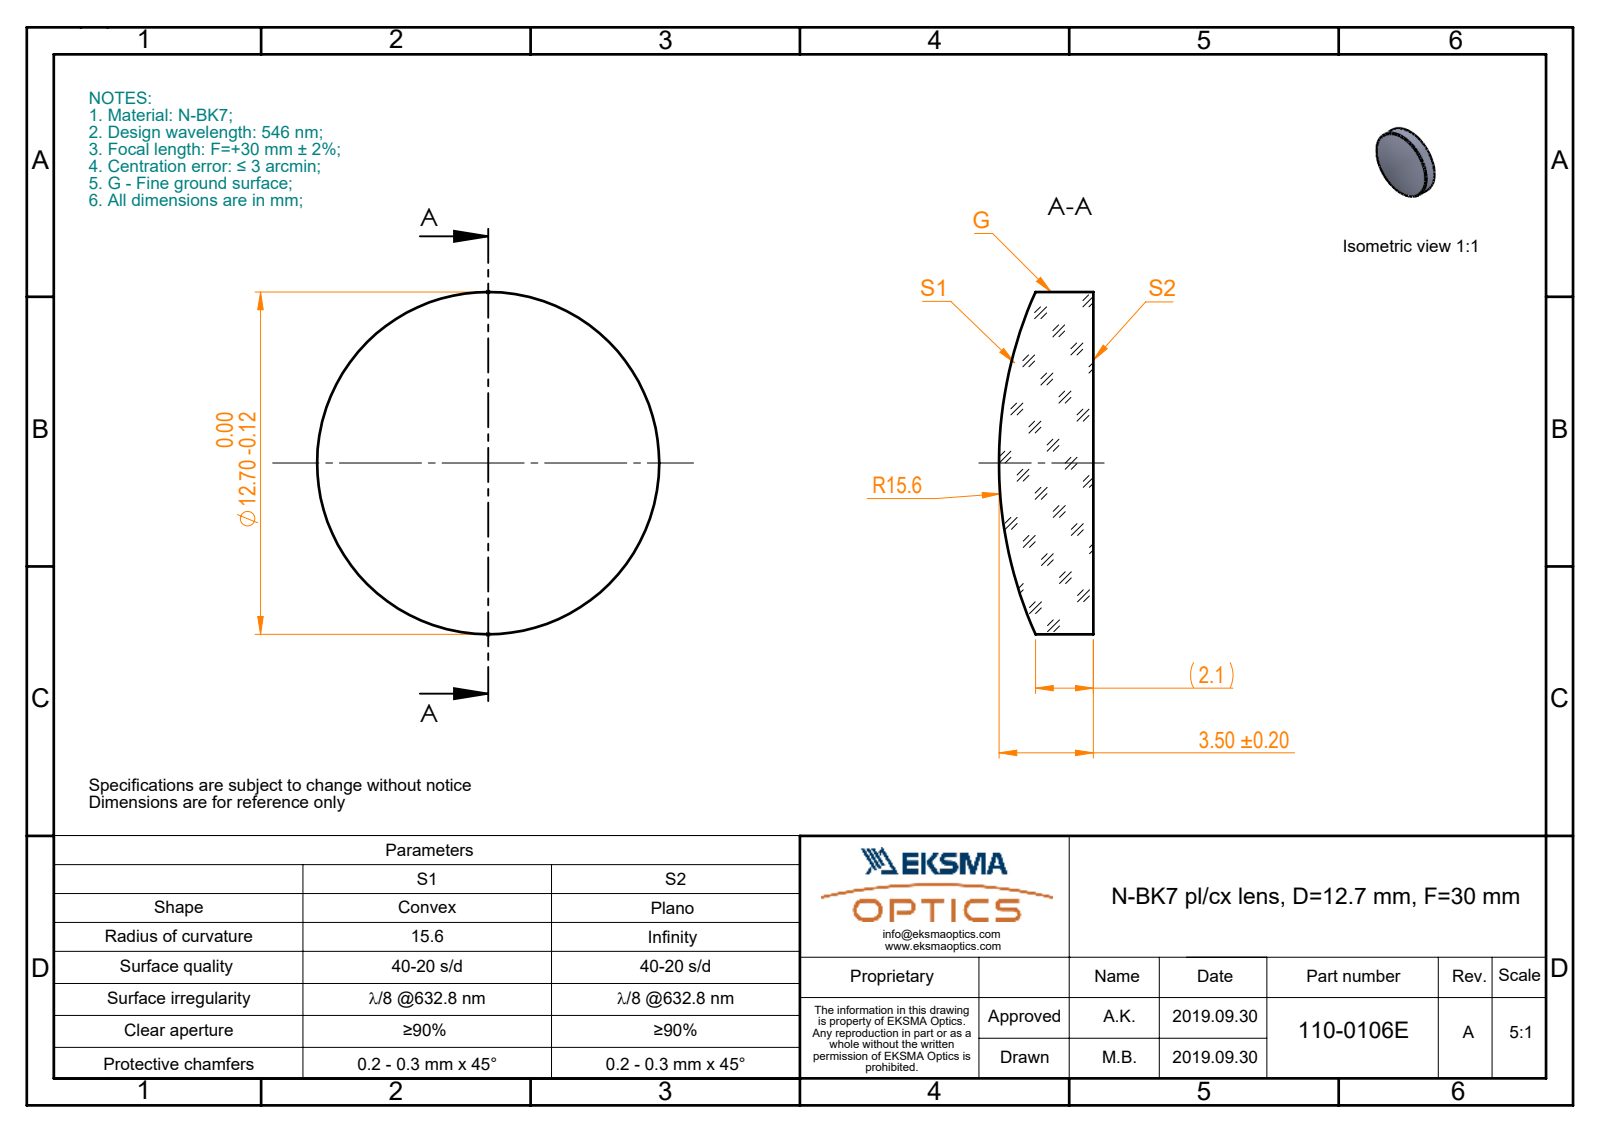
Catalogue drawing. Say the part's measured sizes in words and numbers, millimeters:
The part is named "110-0106E BK7 pl-cx 12.7 F30". Its 3-D file was written by "SolidWorks 2019 (CONFIG_CONTROL_DESIGN)". It is 1 solid with 4 faces: 1 planar, 2 cylindrical and 1 other. Overall it measures 12.7 by 12.7 by 3.5 millimeters. Its volume is 359 cubic millimeters and its surface area 345 square millimeters. Round bosses or shafts: 1 of diameter 12.7.
